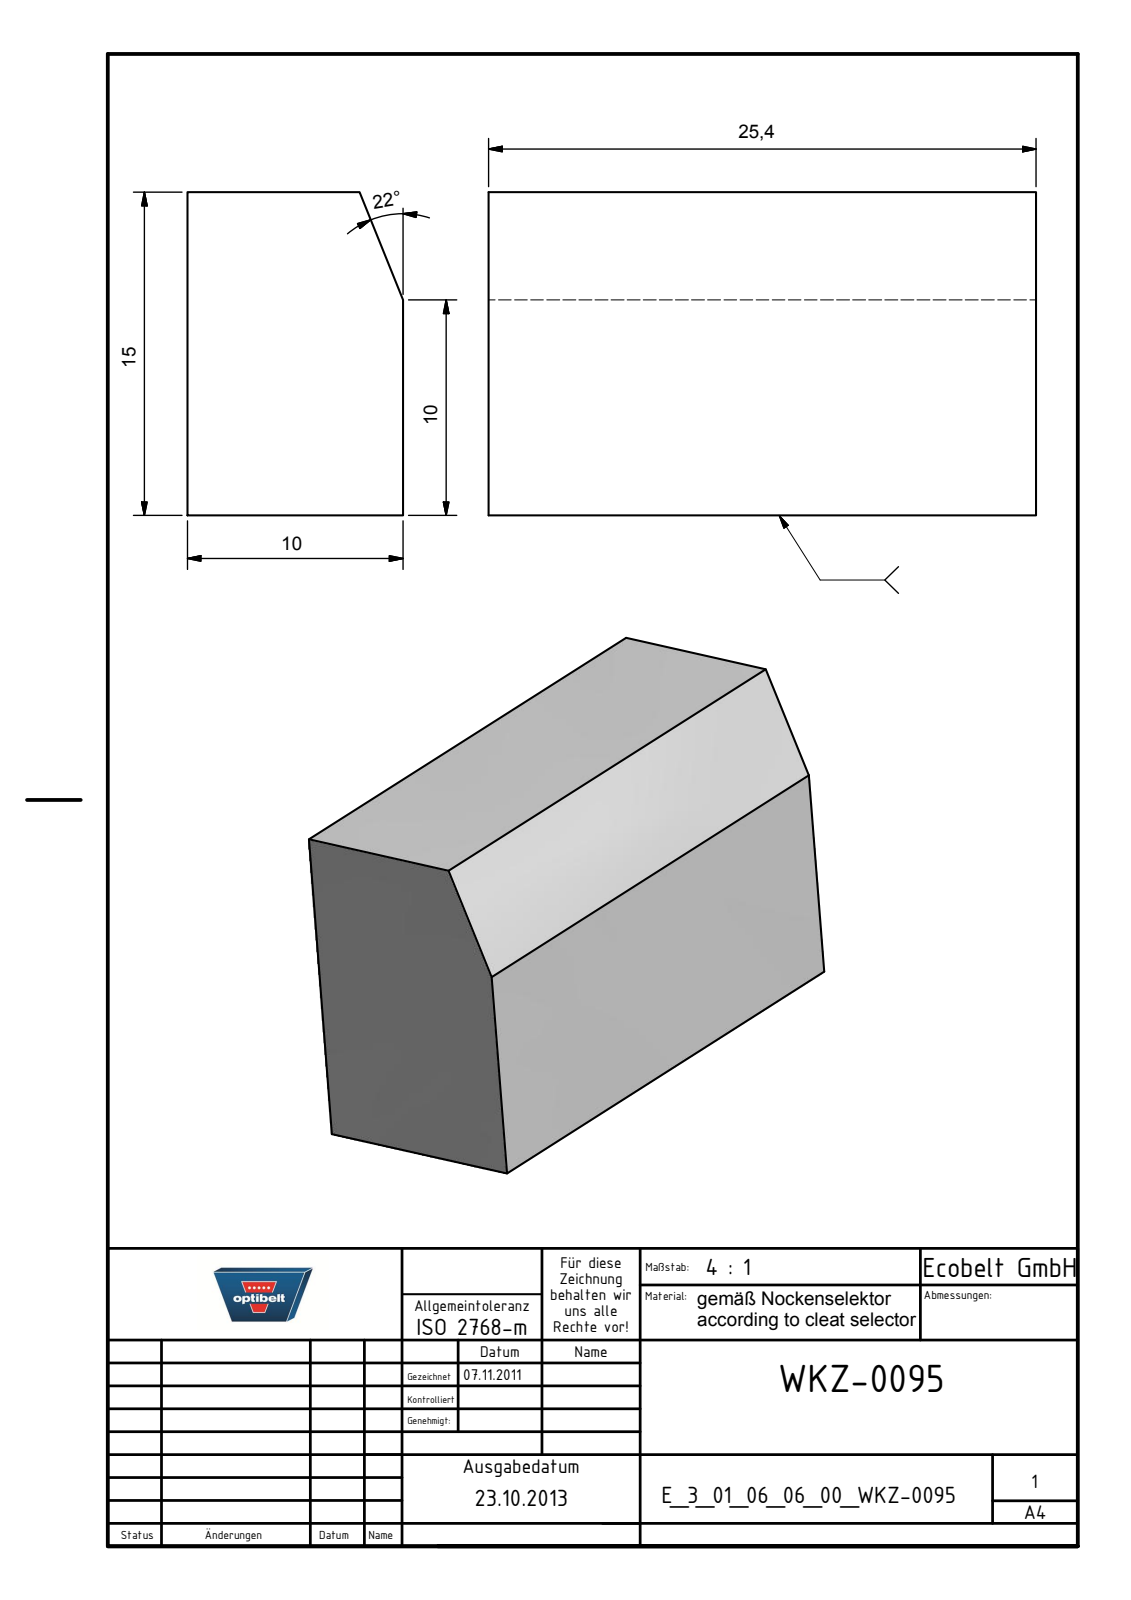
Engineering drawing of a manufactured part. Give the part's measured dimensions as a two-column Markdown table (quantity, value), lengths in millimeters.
| quantity | value |
| --- | --- |
| part name | E_3_01_06_06_00_WKZ-0095 |
| STEP written by | Autodesk Inventor 2025 (AUTOMOTIVE_DESIGN) |
| units | millimeters |
| bodies | 1 solid, 7 faces (7 planar, 0 cylindrical, 0 other) |
| overall size | 25.4 × 15 × 10 |
| volume | 3 682 mm³ |
| surface area | 1 519 mm² |
| main face-to-face distances | 10, 15, 25.4 |
